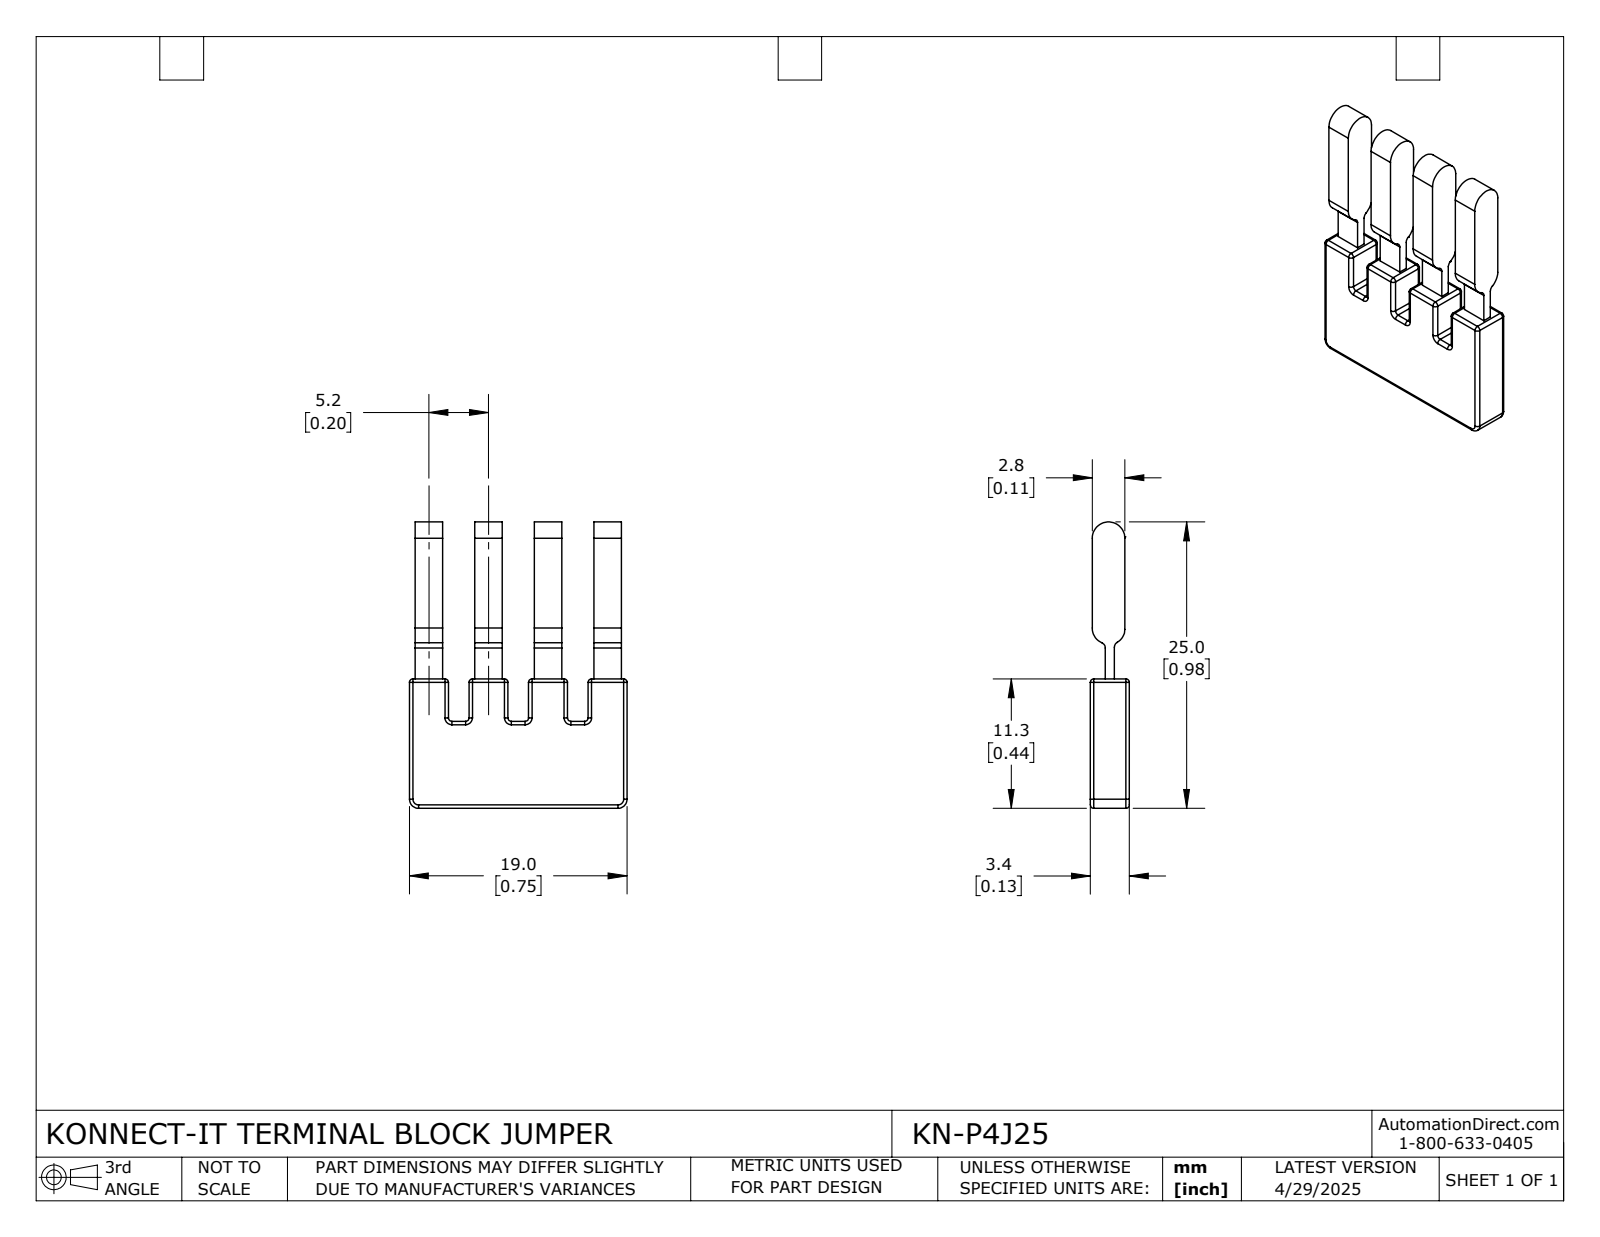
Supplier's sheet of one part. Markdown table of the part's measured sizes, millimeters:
| quantity | value |
| --- | --- |
| part name | KN-P4J25 |
| STEP written by | SolidWorks 2024 (CONFIG_CONTROL_DESIGN) |
| units | millimeters |
| bodies | 1 solid, 152 faces (48 planar, 72 cylindrical, 32 other) |
| overall size | 25 × 19 × 3.4 |
| volume | 957 mm³ |
| surface area | 1 169 mm² |
| partial cylindrical surfaces (radius × count) | 0.3 × 36, 0.5 × 2, 0.8 × 2, 1.43 × 2, 2 × 2, 1.3 × 1 |
| main face-to-face distances | 5.2, 3.4, 10.4, 2.4, 0.5, 2.9, 7.6, 2.8, 5.7, 8.1 |
